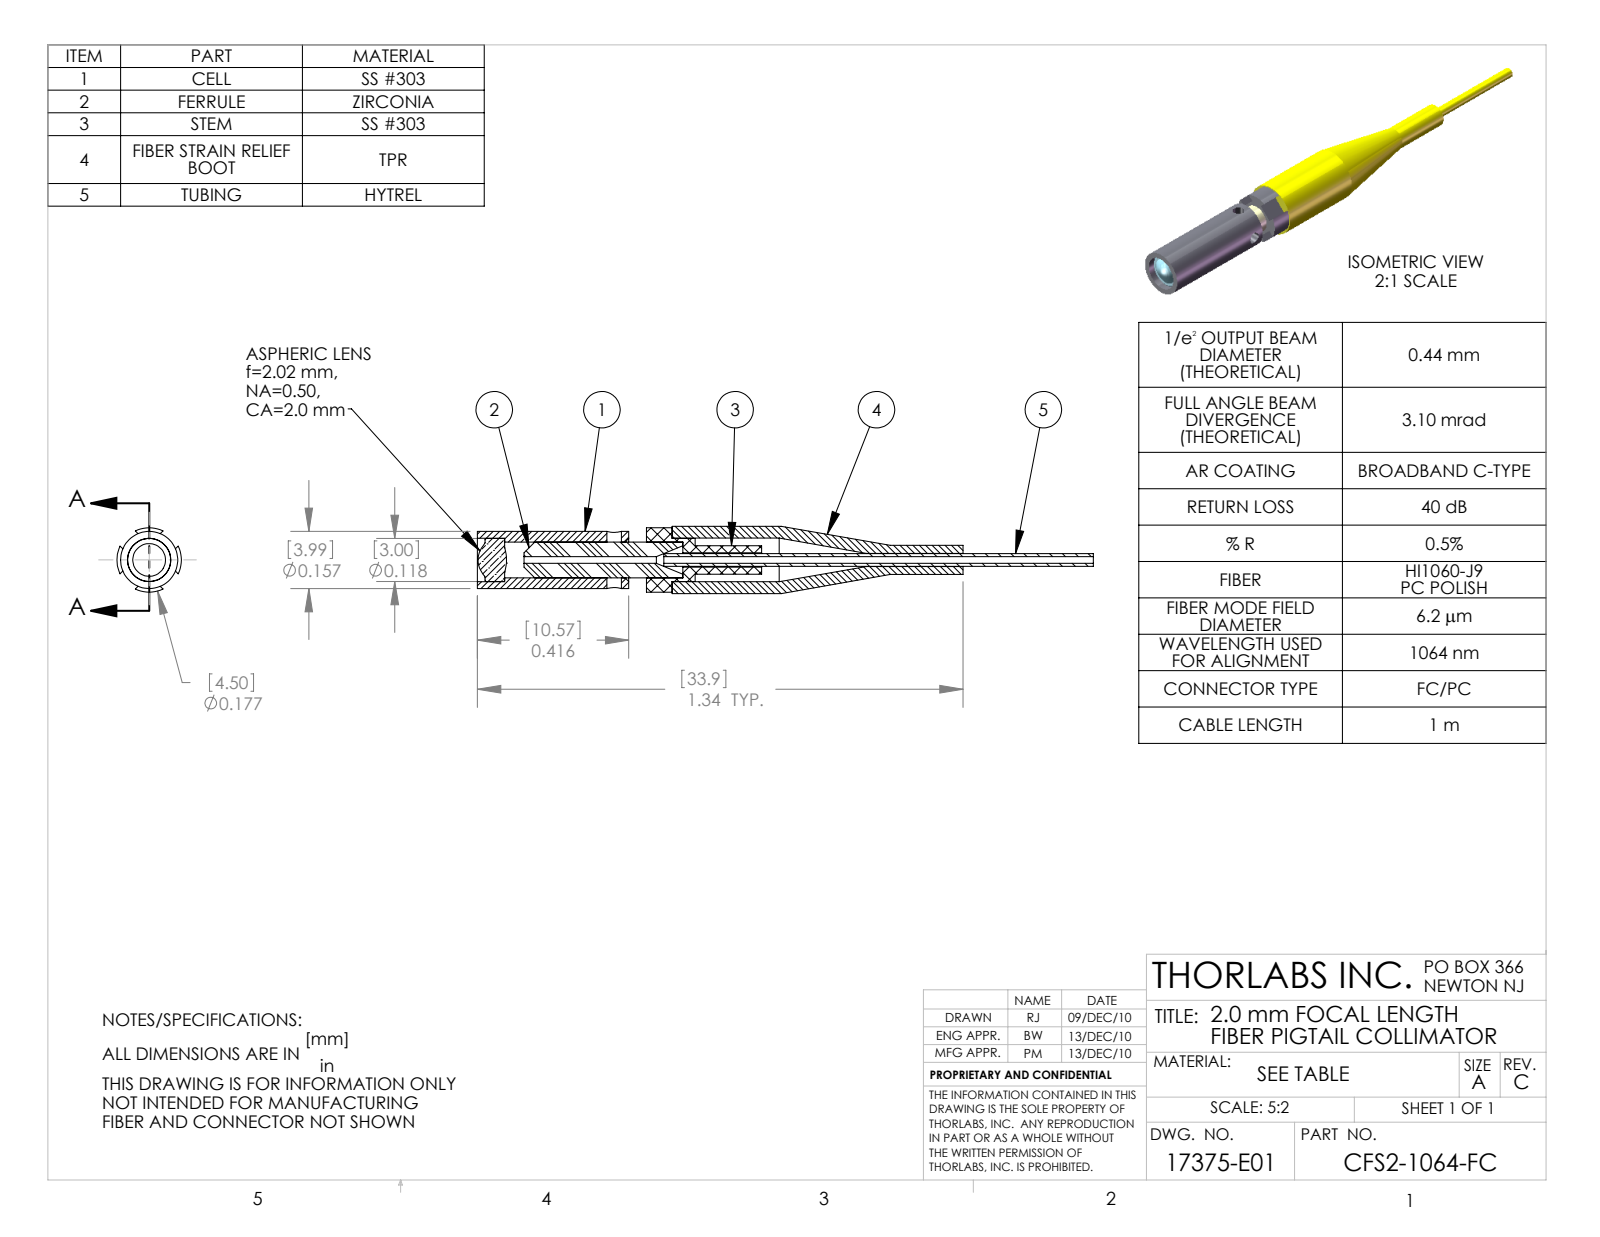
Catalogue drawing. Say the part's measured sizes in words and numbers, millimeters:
The part is named "17375-E0W". Its 3-D file was written by "SolidWorks 2009 (AUTOMOTIVE_DESIGN)". It is 0 solids with 57 faces: 19 planar, 28 cylindrical and 10 other. Overall it measures 43.02 by 4.7 by 4.7 millimeters. Round holes: 2 of diameter 1.02, 1 of diameter 0.46, 1 of diameter 3.02. Round bosses or shafts: 1 of diameter 4.7, 1 of diameter 3.99, 1 of diameter 3, 1 of diameter 2.5, 1 of diameter 2.03, 1 of diameter 0.9. Partial cylindrical surfaces (rounded edges, fillets, slot ends): 1 of radius 2.25. The main face-to-face distances are 2.25, 0.75, 1.8, 3, 3.03, 1.23, 13.6, 11.8, 10.57, 1.5.
